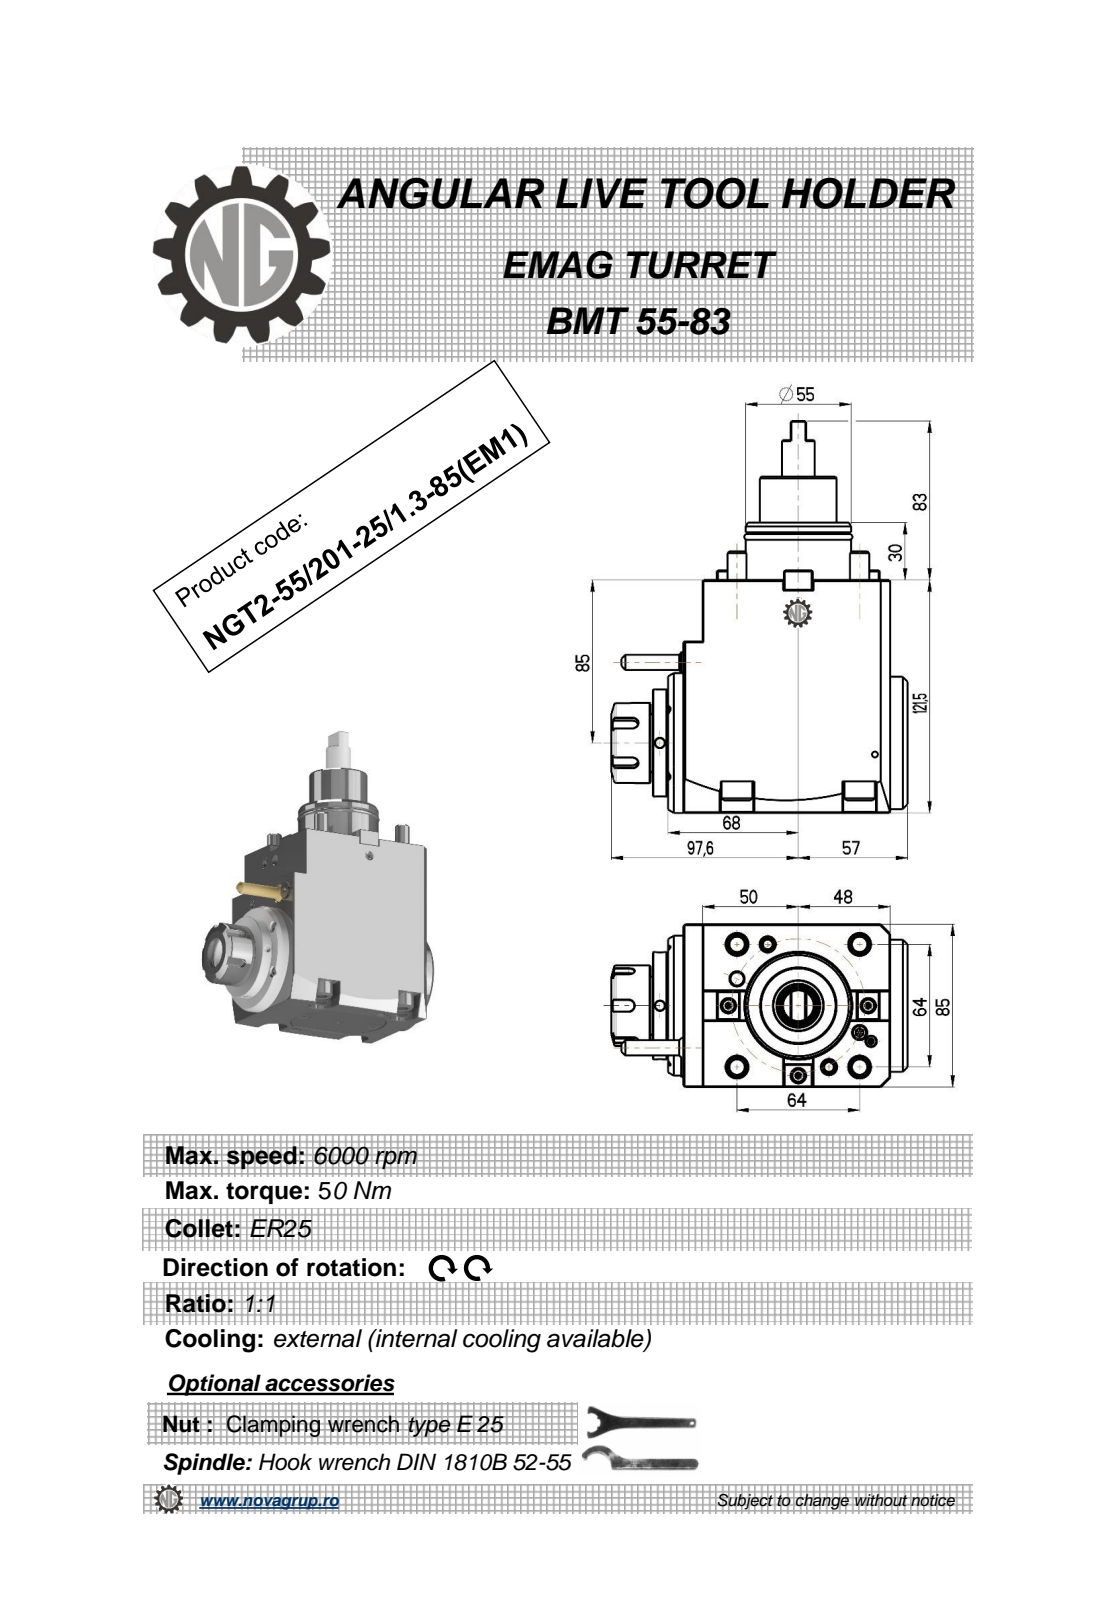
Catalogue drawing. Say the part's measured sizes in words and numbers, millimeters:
The part is named "NGT2_55_201_25_1_3_85_EM1". Its 3-D file was written by "PRO/ENGINEER BY PARAMETRIC TECHNOLOGY CORPORATION, 2010280 (CONFIG_CONTROL_DESIGN)". It is 2 solids with 482 faces: 228 planar, 109 cylindrical and 145 other. Overall it measures 204.5 by 154.6 by 85 millimeters. Its volume is 1 282 000 cubic millimeters and its surface area 110 439 square millimeters. Round holes: 3 of diameter 5, 2 of diameter 6.8, 1 of diameter 3, 1 of diameter 12. Round bosses or shafts: 4 of diameter 16, 4 of diameter 10, 1 of diameter 73, 1 of diameter 69, 1 of diameter 56, 1 of diameter 55, 1 of diameter 50, 1 of diameter 43.4. Partial cylindrical surfaces (rounded edges, fillets, slot ends): 20 of radius 0.32, 6 of radius 0.22, 5 of radius 3, 4 of radius 8.5, 2 of radius 0.8, 2 of radius 480. The main face-to-face distances are 85, 121.5, 8, 9, 10, 108, 117, 107, 98, 116. The hole center spacings are 42.62, 69.86, 105.19.
